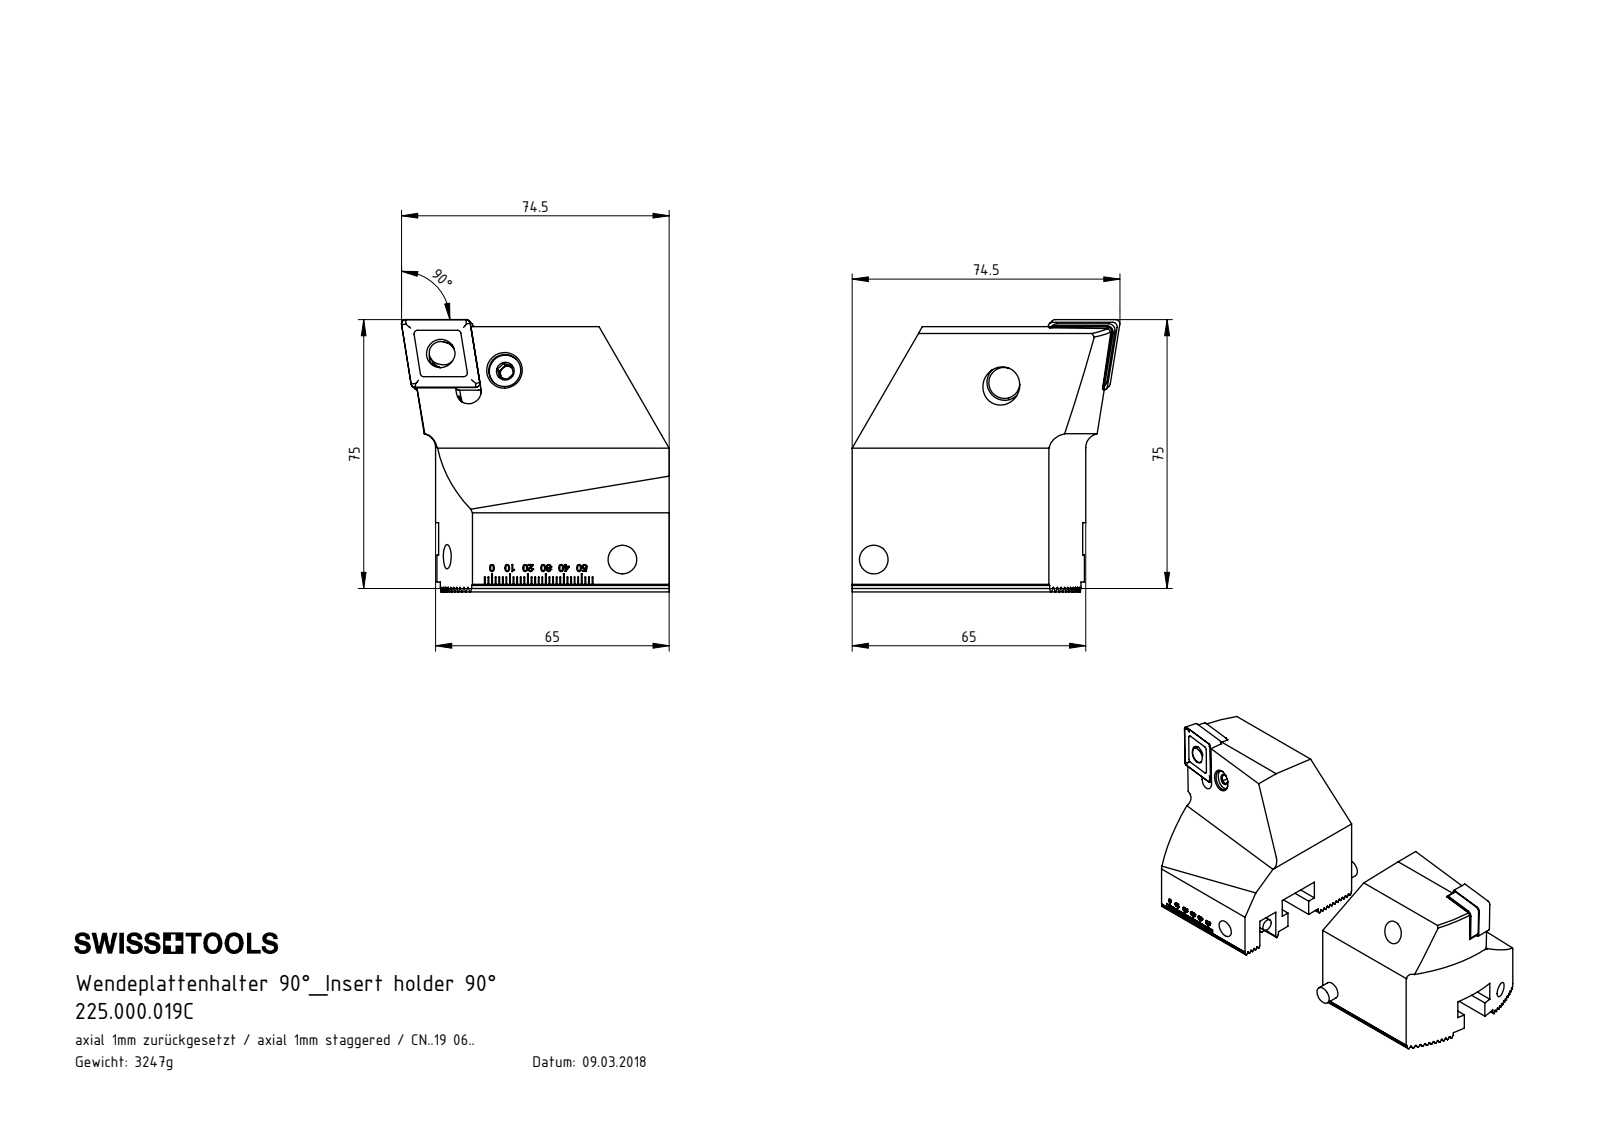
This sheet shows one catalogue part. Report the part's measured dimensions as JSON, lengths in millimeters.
{"part_name": "WCF; WCF-ER3.101.000_A; ISO 4028 - M8 x 35; WCF-ER1.101.000 (+6 more)", "step_written_by": "SolidWorks 2017 (CONFIG_CONTROL_DESIGN)", "units": "millimeters", "bodies": {"solids": 16, "faces": 1300, "planar": 784, "cylindrical": 170, "other": 346}, "overall_size": [200.04, 83.92, 75.79], "volume_mm3": 410334, "surface_area_mm2": 73404, "round_holes": [[8, 4], [6.8, 2], [7.94, 2], [9, 2], [9.6, 2], [10.2, 2]], "round_bosses_or_shafts": [[10, 2], [9.9, 2], [8.6, 2], [8, 2], [5.5, 2], [4.45, 2]], "partial_cylinders_radius": [[0.14, 22], [1.2, 8], [1.8, 8], [4.15, 8], [4.7, 3], [3.1, 2], [3.5, 2], [3.65, 2]], "face_to_face_distances": [1.73, 6.93, 8.66, 70, 3.46, 5.2, 41.57, 43.3, 24.5, 45.5], "hole_center_spacings": [7, 18.52, 70, 0.31, 0.32, 18.8, 18.81, 40]}
